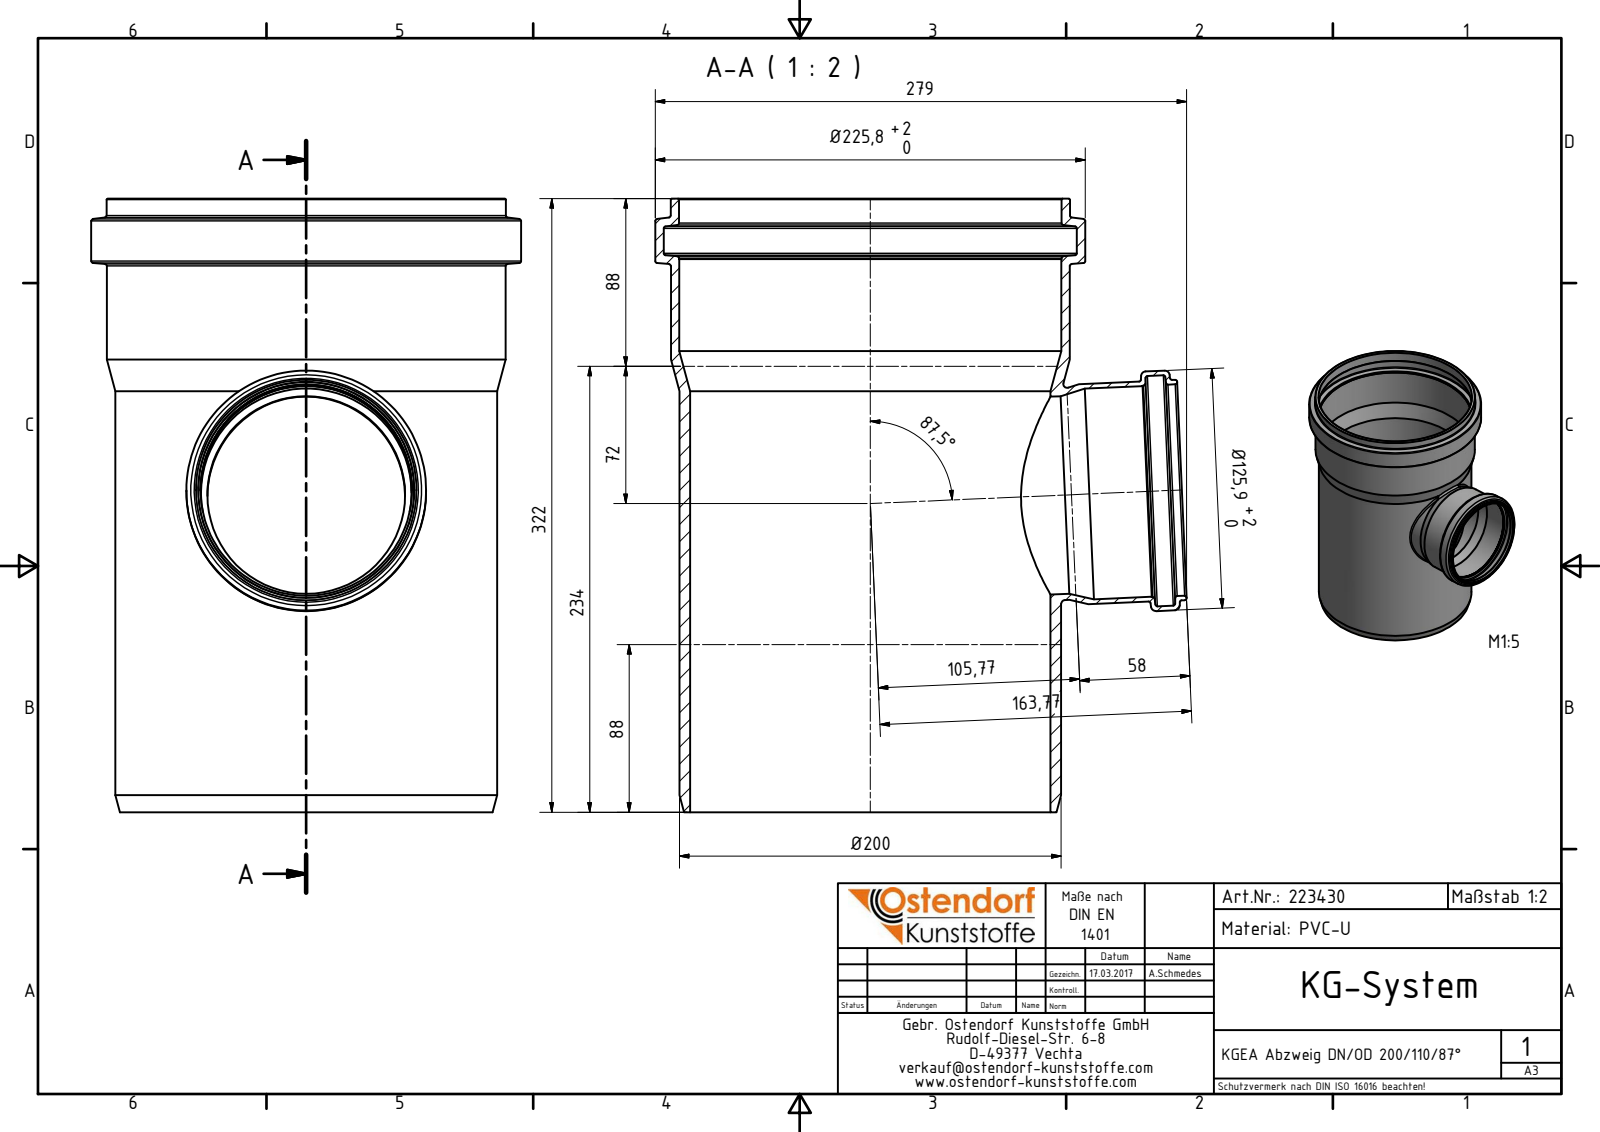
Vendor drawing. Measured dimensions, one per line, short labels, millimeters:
name: 223430 KGEA Abzweig DN_OD 200_110_87°
written by: Autodesk Inventor 2016 (AUTOMOTIVE_DESIGN)
unit: mm
bodies: 1 solid, 58 faces (5 planar, 18 cylindrical, 35 other)
size: 322 × 279 × 225.8
volume: 1 123 000 mm³; area: 465 582 mm²
holes: 1× ⌀103.8, 1× ⌀110.7, 1× ⌀111, 1× ⌀121.1, 1× ⌀189.3, 1× ⌀200.6, 1× ⌀200.9, 1× ⌀217
bosses: 1× ⌀225.8, 1× ⌀209.7, 1× ⌀209.4, 1× ⌀200.5, 1× ⌀125.9, 1× ⌀115.8, 1× ⌀115.5, 1× ⌀110.2
face distances: 322, 290.23, 31.77, 18.2
